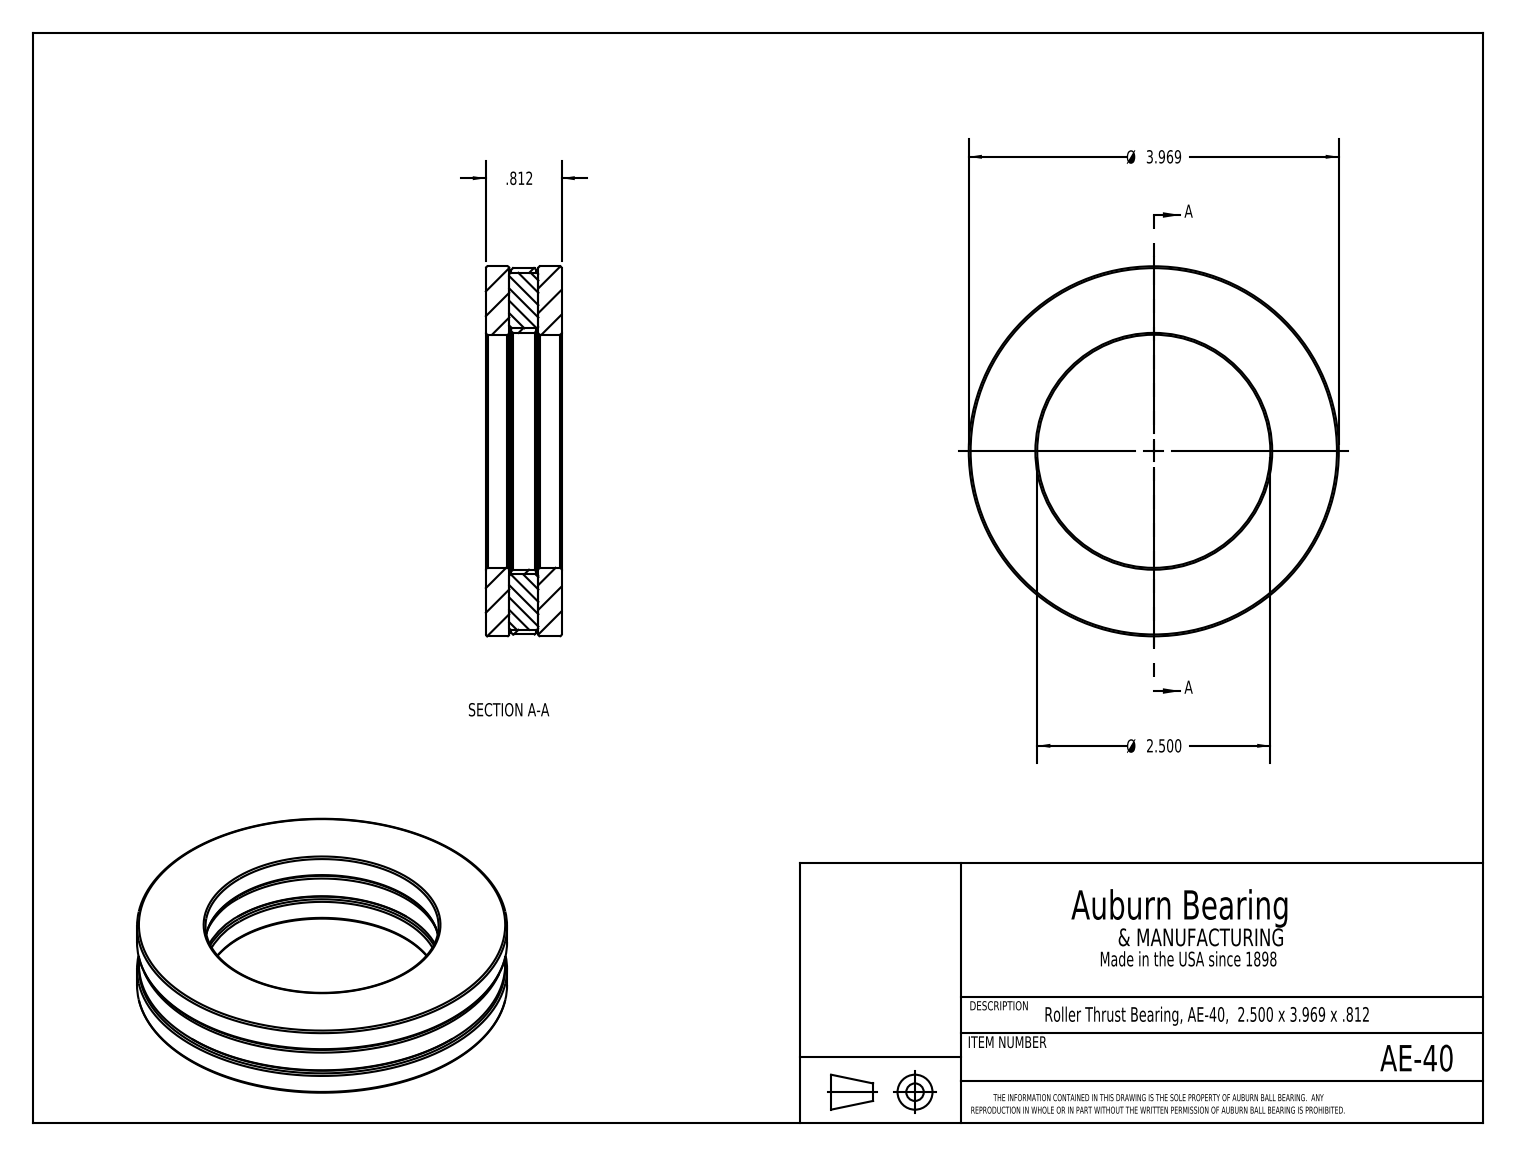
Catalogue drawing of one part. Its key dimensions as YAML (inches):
part_name: "AE-40"
step_written_by: "SolidWorks 2017 (CONFIG_CONTROL_DESIGN)"
units: inches
bodies: {solids: 7, faces: 60, planar: 30, cylindrical: 10, other: 20}
overall_size: [3.969, 3.969, 0.812]
volume: 5.614
surface_area: 61.84
round_holes:
  - {diameter: 2.5, count: 1}
  - {diameter: 2.54, count: 1}
round_bosses_or_shafts:
  - {diameter: 0.312, count: 2}
  - {diameter: 3.969, count: 1}
  - {diameter: 3.929, count: 1}
face_to_face_distances: [0.25, 0.562, 0.27, 0.542, 0.02, 0.292, 0.312, 0.812, 0.272, 1.164]
